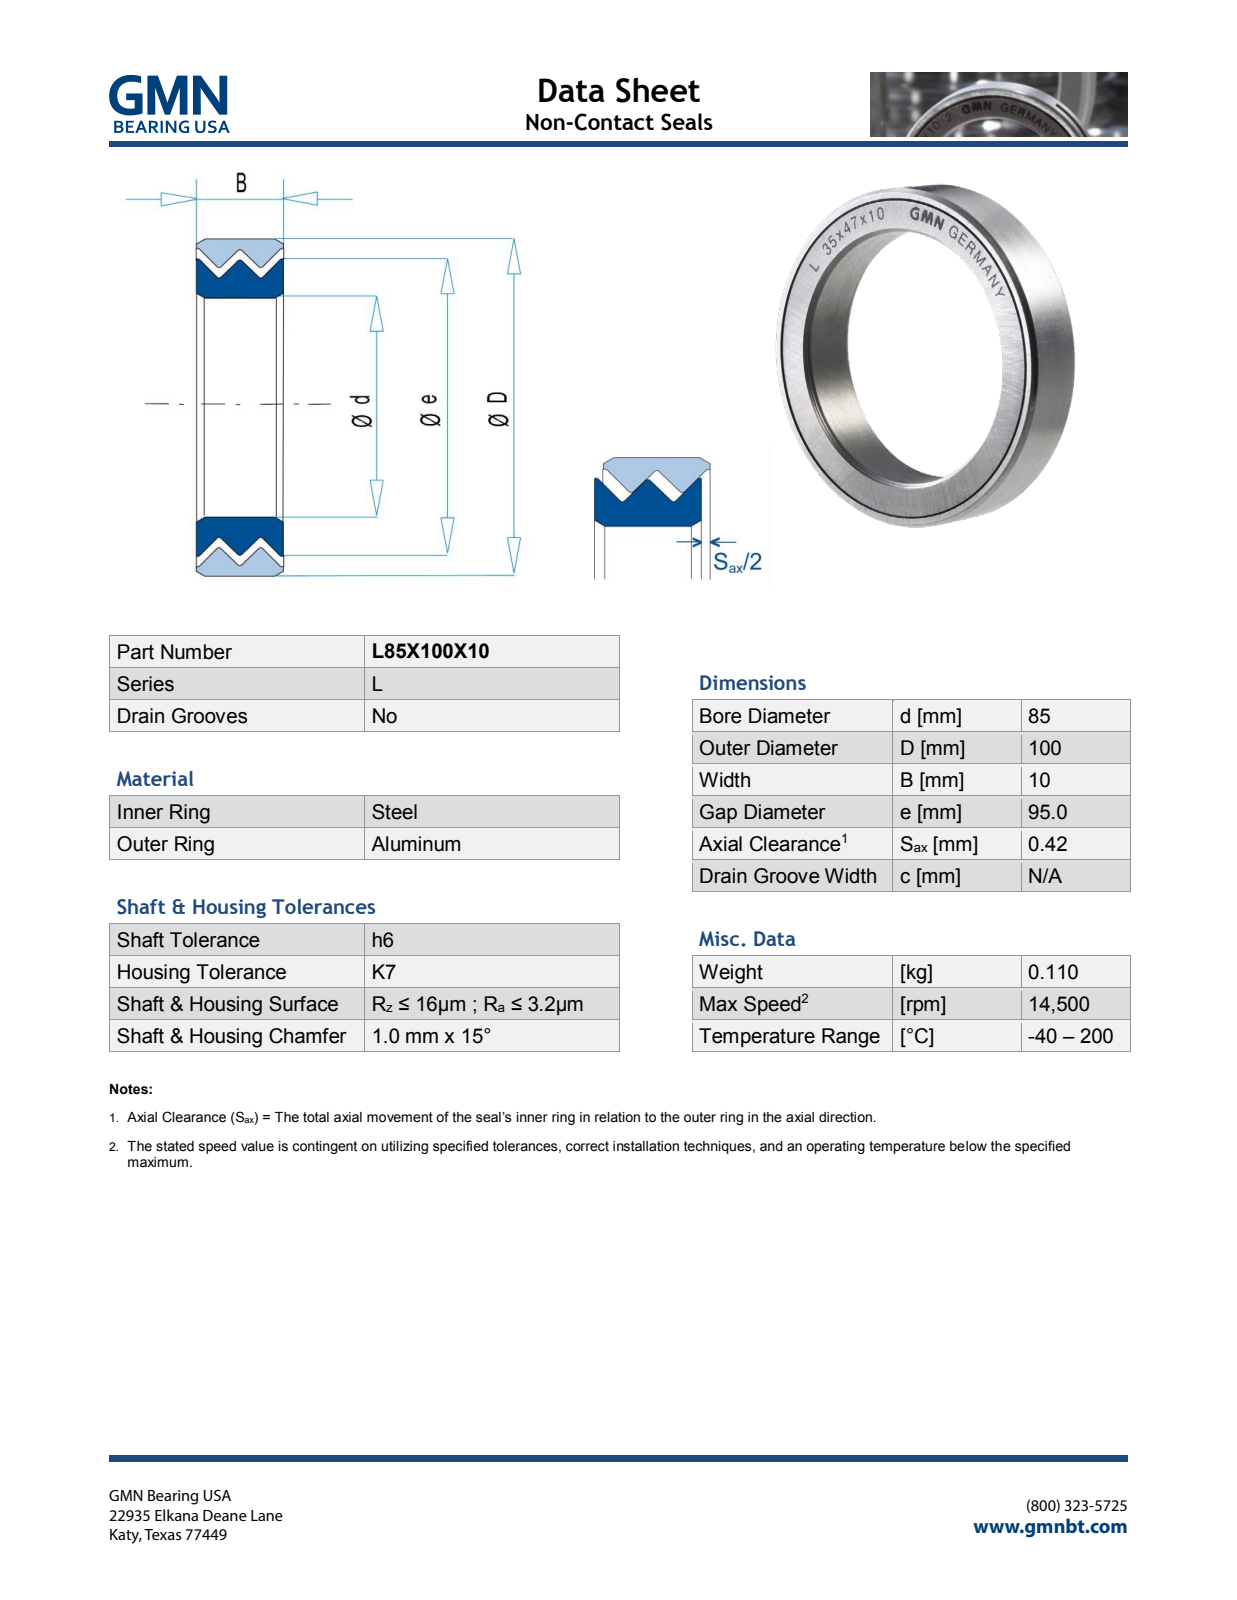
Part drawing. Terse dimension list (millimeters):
name: L85X100X10_PRT
written by: PRO/ENGINEER BY PARAMETRIC TECHNOLOGY CORPORATION, 2013150 (AUTOMOTIVE_DESIGN)
unit: mm
bodies: 2 solids, 631 faces (575 planar, 12 cylindrical, 44 other)
size: 100 × 100 × 10.07
volume: 20 882 mm³; area: 17 421 mm²
holes: 1× ⌀85, 1× ⌀95.3
bosses: 1× ⌀100, 1× ⌀95
face distances: 10, 10.07, 0.31, 2.42, 2.12, 1.82, 2.11, 2.02, 1.08, 1.72
